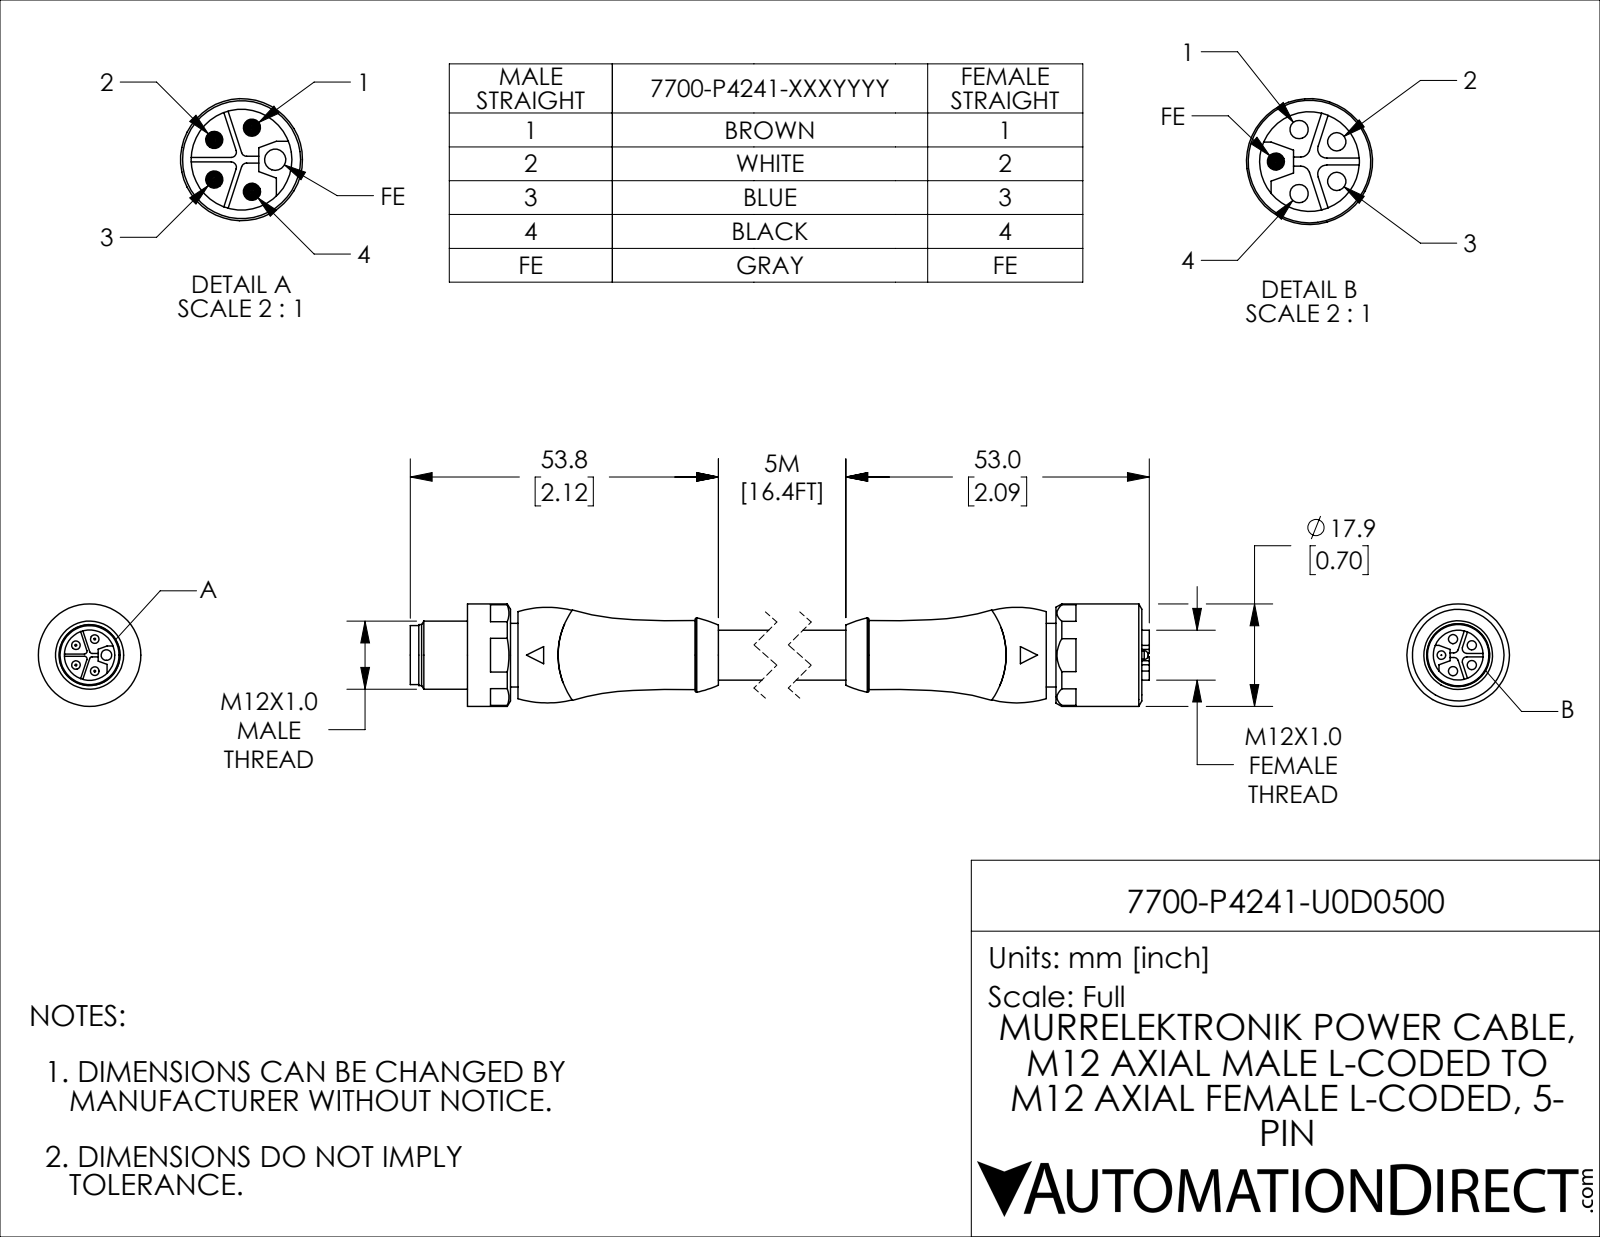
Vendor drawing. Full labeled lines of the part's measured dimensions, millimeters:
Part name (STEP PRODUCT): 7700-P4241-U0D0500_1; 7700-P4241-U0D0500_2; 7700-P4241-U0D0500
STEP written by: SolidWorks 2021 (CONFIG_CONTROL_DESIGN)
Units: millimetres
Bodies: 3 solids, 214 faces (98 planar, 62 cylindrical, 54 other)
Overall size (bounding box): 136.8 × 17.9 × 17.9
Volume: 17 860 mm³ · Surface area: 9 316 mm²
Round holes (diameter × count): ⌀1.6 ×4, ⌀1.9 ×1, ⌀8.8 ×1, ⌀11 ×1, ⌀13 ×1
Round bosses / shafts (diameter × count): ⌀1.5 ×5, ⌀17.9 ×1, ⌀13 ×1, ⌀11.9 ×1, ⌀11.1 ×1, ⌀10.6 ×1, ⌀10.3 ×1, ⌀8.7 ×1
Partial cylindrical surfaces — rounded edges, fillets, slot ends (radius × count): R0.5 ×4, R0.8 ×4
Main face-to-face distances: 108.8, 1.7, 8.8, 16.9, 1.3, 7.5, 5.8, 125.5, 16.7, 110.5
Hole centre spacings: 2.9, 3.5, 5.6, 5.6
